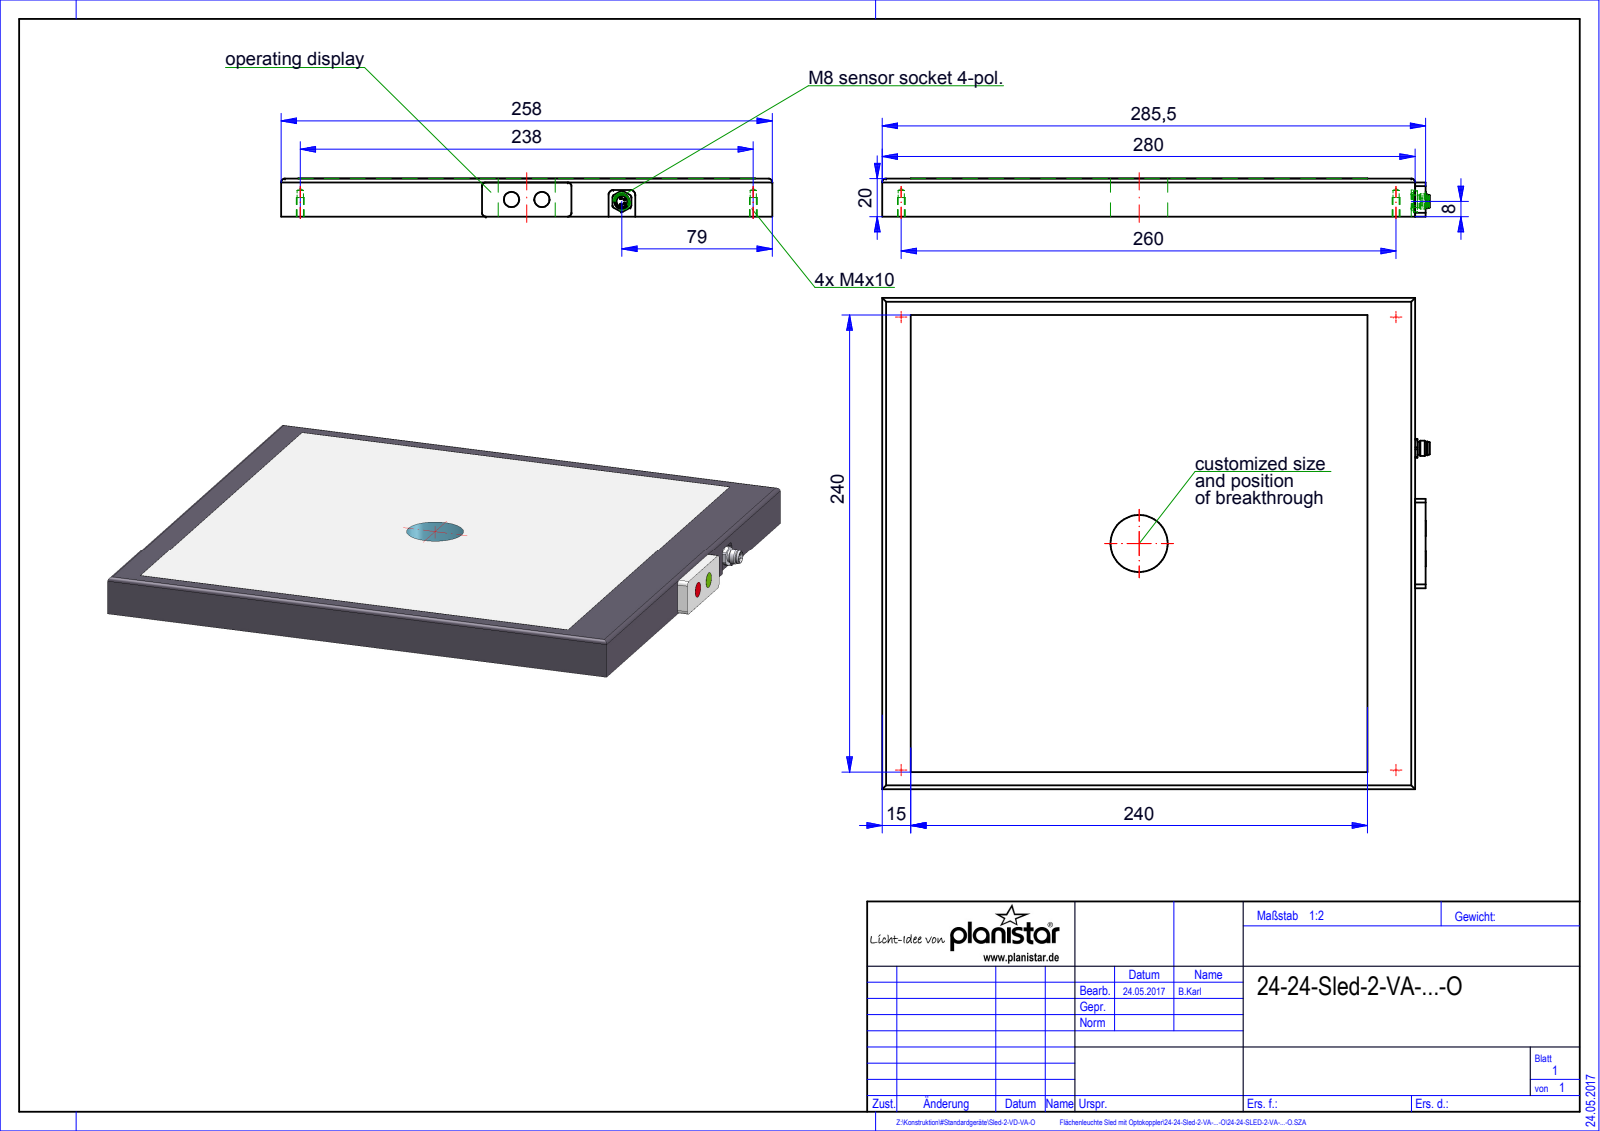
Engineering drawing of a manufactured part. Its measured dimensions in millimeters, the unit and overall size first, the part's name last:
Units: millimetres
Overall size (bounding box): 287.7 × 258 × 20.1
Round holes (diameter × count): ⌀3.3 ×4, ⌀4 ×4, ⌀5.8 ×1, ⌀30 ×1
Round bosses / shafts (diameter × count): ⌀1 ×4, ⌀8 ×3, ⌀7.2 ×1, ⌀6.8 ×1, ⌀6.4 ×1
Partial cylindrical surfaces — rounded edges, fillets, slot ends (radius × count): R2 ×8, R2.5 ×2, R5.5 ×1
Main face-to-face distances: 20.1, 20, 258, 280, 285.5, 5.5, 2, 2.1, 18, 278
Hole centre spacings: 172.59, 179.96, 238, 260, 352.48
Volume: 1 439 000 mm³ · Surface area: 169 383 mm²
Bodies: 3 solids, 90 faces (39 planar, 38 cylindrical, 13 other)
Part name (STEP PRODUCT): Root; Baugruppe_Xled-2-VD; QUADER_0; 09-3391-00-04
STEP written by: HiCAD 2015 2002.1 Build 408 (AUTOMOTIVE_DESIGN)
